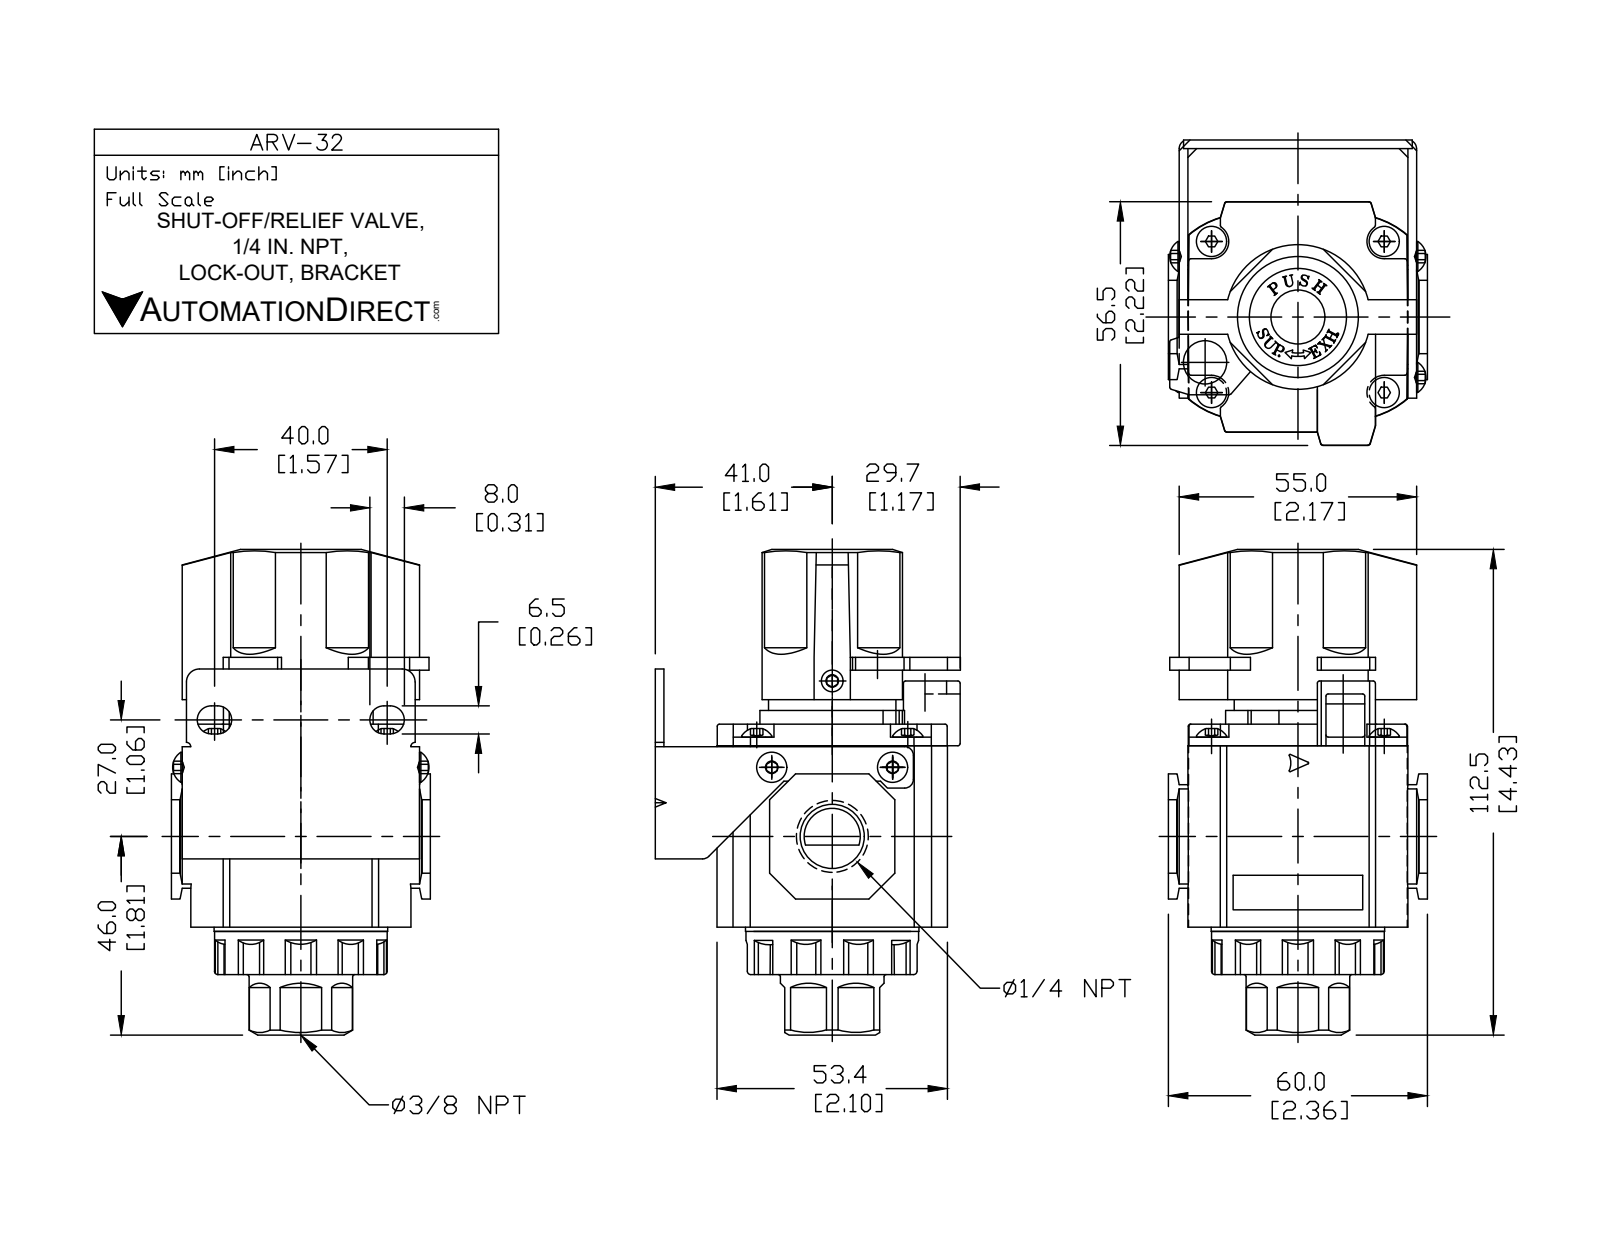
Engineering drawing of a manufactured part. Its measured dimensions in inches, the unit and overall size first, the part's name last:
Units: inches
Overall size (bounding box): 4.429 × 2.783 × 2.4
Round holes (diameter × count): ⌀0.394 ×1, ⌀0.438 ×1, ⌀0.923 ×1
Round bosses / shafts (diameter × count): ⌀0.276 ×6, ⌀1.575 ×1, ⌀1.543 ×1, ⌀1.319 ×1, ⌀0.953 ×1, ⌀0.659 ×1
Partial cylindrical surfaces — rounded edges, fillets, slot ends (radius × count): R0.059 ×6, R0.128 ×4, R0.193 ×4, R0.039 ×2, R0.079 ×2, R0.118 ×2, R0.197 ×1, R0.468 ×1
Main face-to-face distances: 0.079, 1.654, 0.161, 1.815, 2.087, 2.008, 0.563, 2.665, 0.484, 2.587
Hole centre spacings: 0.942
Volume: 11.73 in³ · Surface area: 74.65 in²
Bodies: 18 solids, 418 faces (290 planar, 83 cylindrical, 45 other)
Part name (STEP PRODUCT): ARV-32
STEP written by: SolidWorks 2015 (CONFIG_CONTROL_DESIGN)
